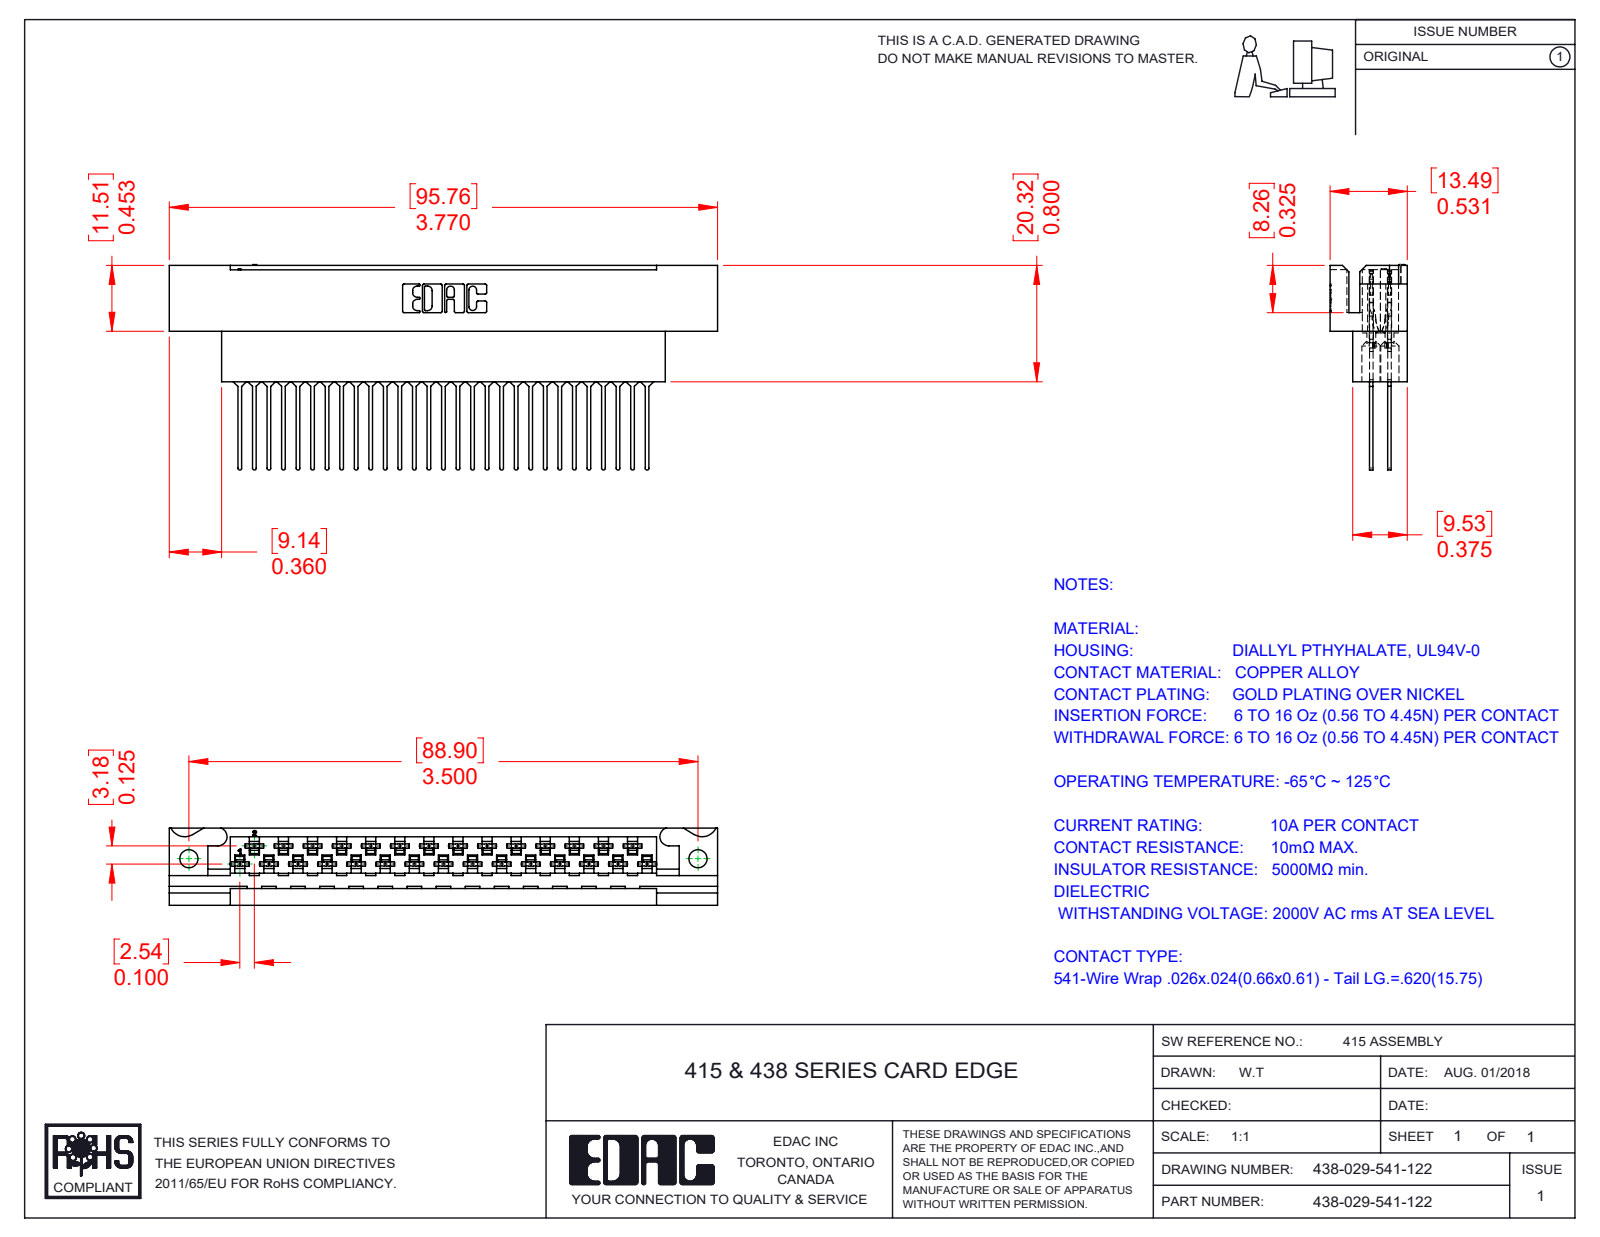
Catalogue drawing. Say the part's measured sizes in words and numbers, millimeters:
The part is named "438-029-541-122; 516-290-001_541; 438-210-001_438-210-029-112". Its 3-D file was written by "SolidWorks 2016 (CONFIG_CONTROL_DESIGN)". It is 30 solids with 2998 faces: 1911 planar, 804 cylindrical and 283 other. Overall it measures 95.76 by 35.85 by 13.49 millimeters. Its volume is 15 636 cubic millimeters and its surface area 19 762 square millimeters. Round holes: 29 of diameter 1.27, 29 of diameter 3.3, 1 of diameter 3.17, 1 of diameter 3.18. Partial cylindrical surfaces (rounded edges, fillets, slot ends): 116 of radius 0.3, 116 of radius 0.56, 58 of radius 0.18, 58 of radius 0.2, 58 of radius 0.41, 58 of radius 2.03, 29 of radius 0.33, 22 of radius 0.25. The main face-to-face distances are 3.18, 0.61, 1.88, 1.27, 7.49, 13.49, 2.92, 3.96, 6.61, 6.88. The hole center spacings are 5.08, 10.16, 15.24, 20.32, 25.4, 30.48, 35.56, 2.54.
